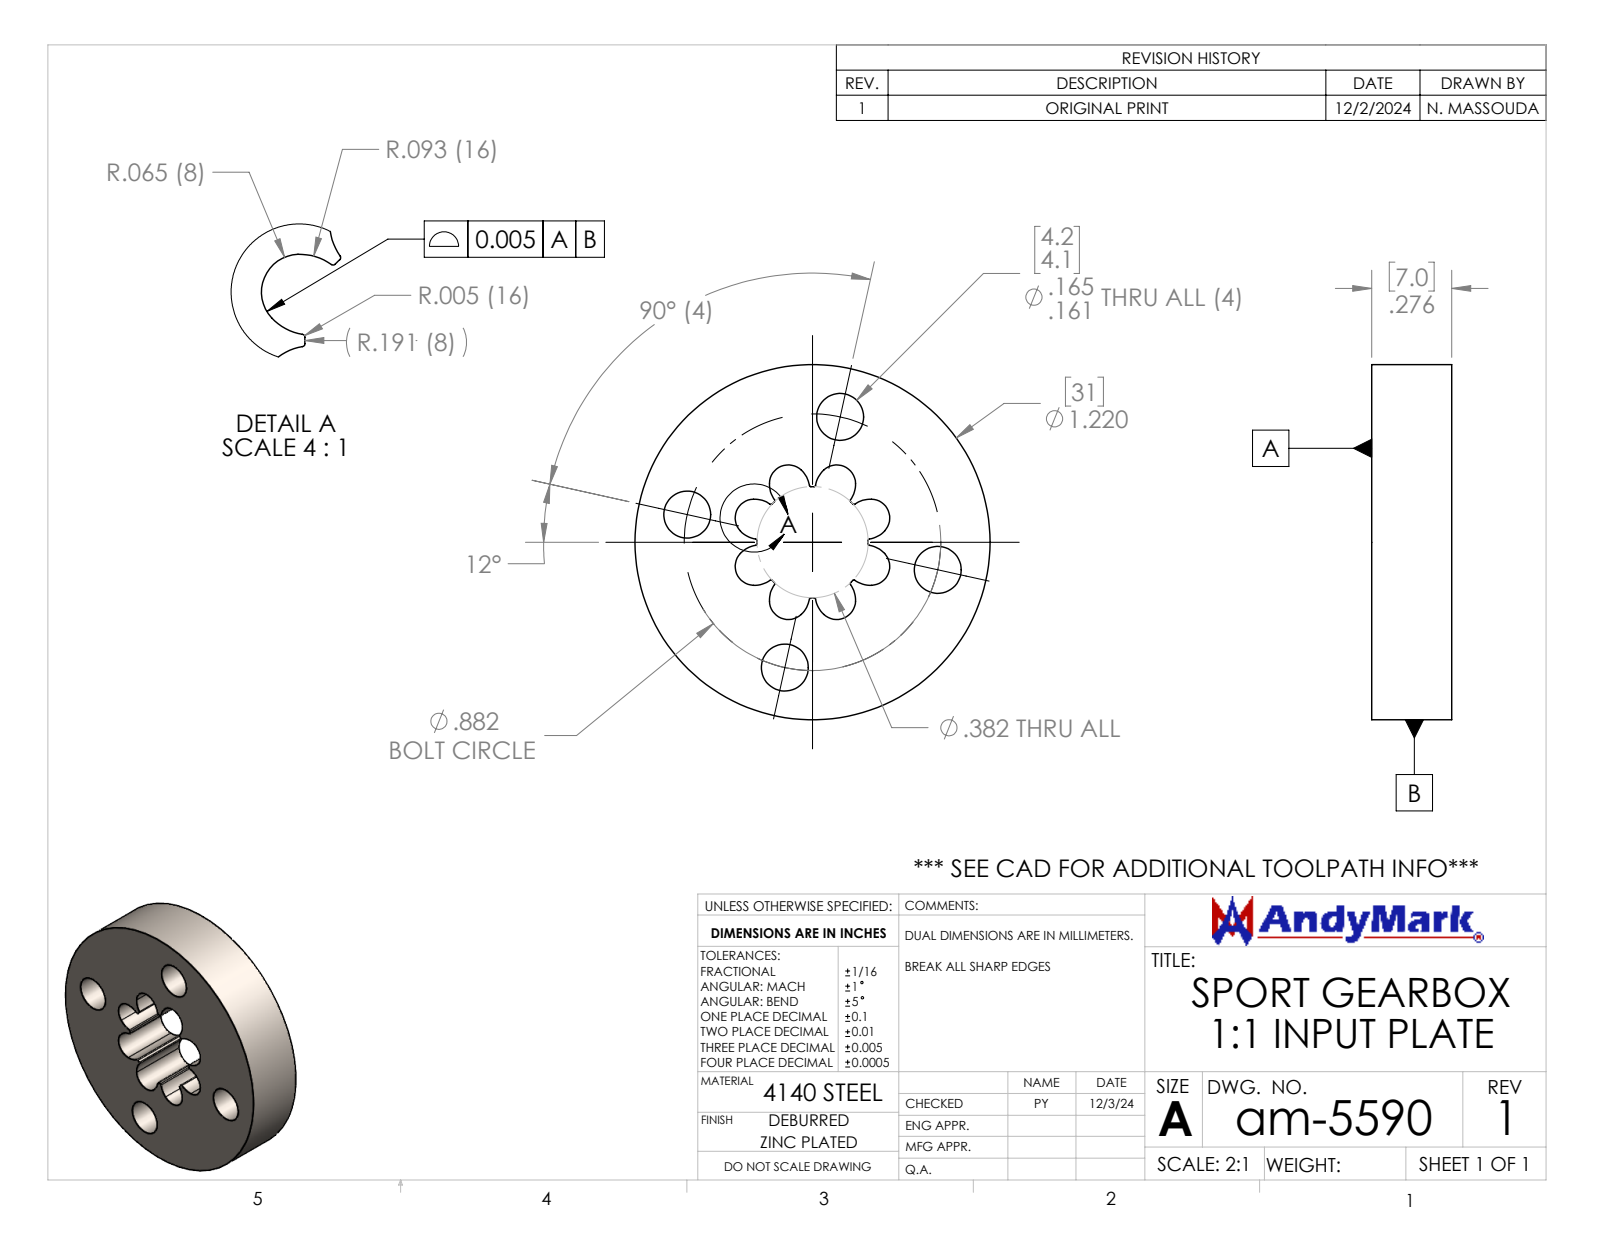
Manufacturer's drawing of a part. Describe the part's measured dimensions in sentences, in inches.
The part is named "am-5590 Sport Gearbox 1-1 Input Plate". Its 3-D file was written by "SolidWorks 2024 (AUTOMOTIVE_DESIGN)". It is 1 solid with 69 faces: 2 planar, 67 cylindrical and 0 other. Overall it measures 1.22 by 1.22 by 0.276 inches. Its volume is 0.245 cubic inches and its surface area 4.045 square inches. Round holes: 4 of diameter 0.161. Round bosses or shafts: 1 of diameter 1.22. Partial cylindrical surfaces (rounded edges, fillets, slot ends): 16 of radius 0.005, 16 of radius 0.093, 8 of radius 0.065, 1 of radius 0.191. The main face-to-face distances are 0.276. The hole center spacings are 0.624, 0.881, 0.882.
